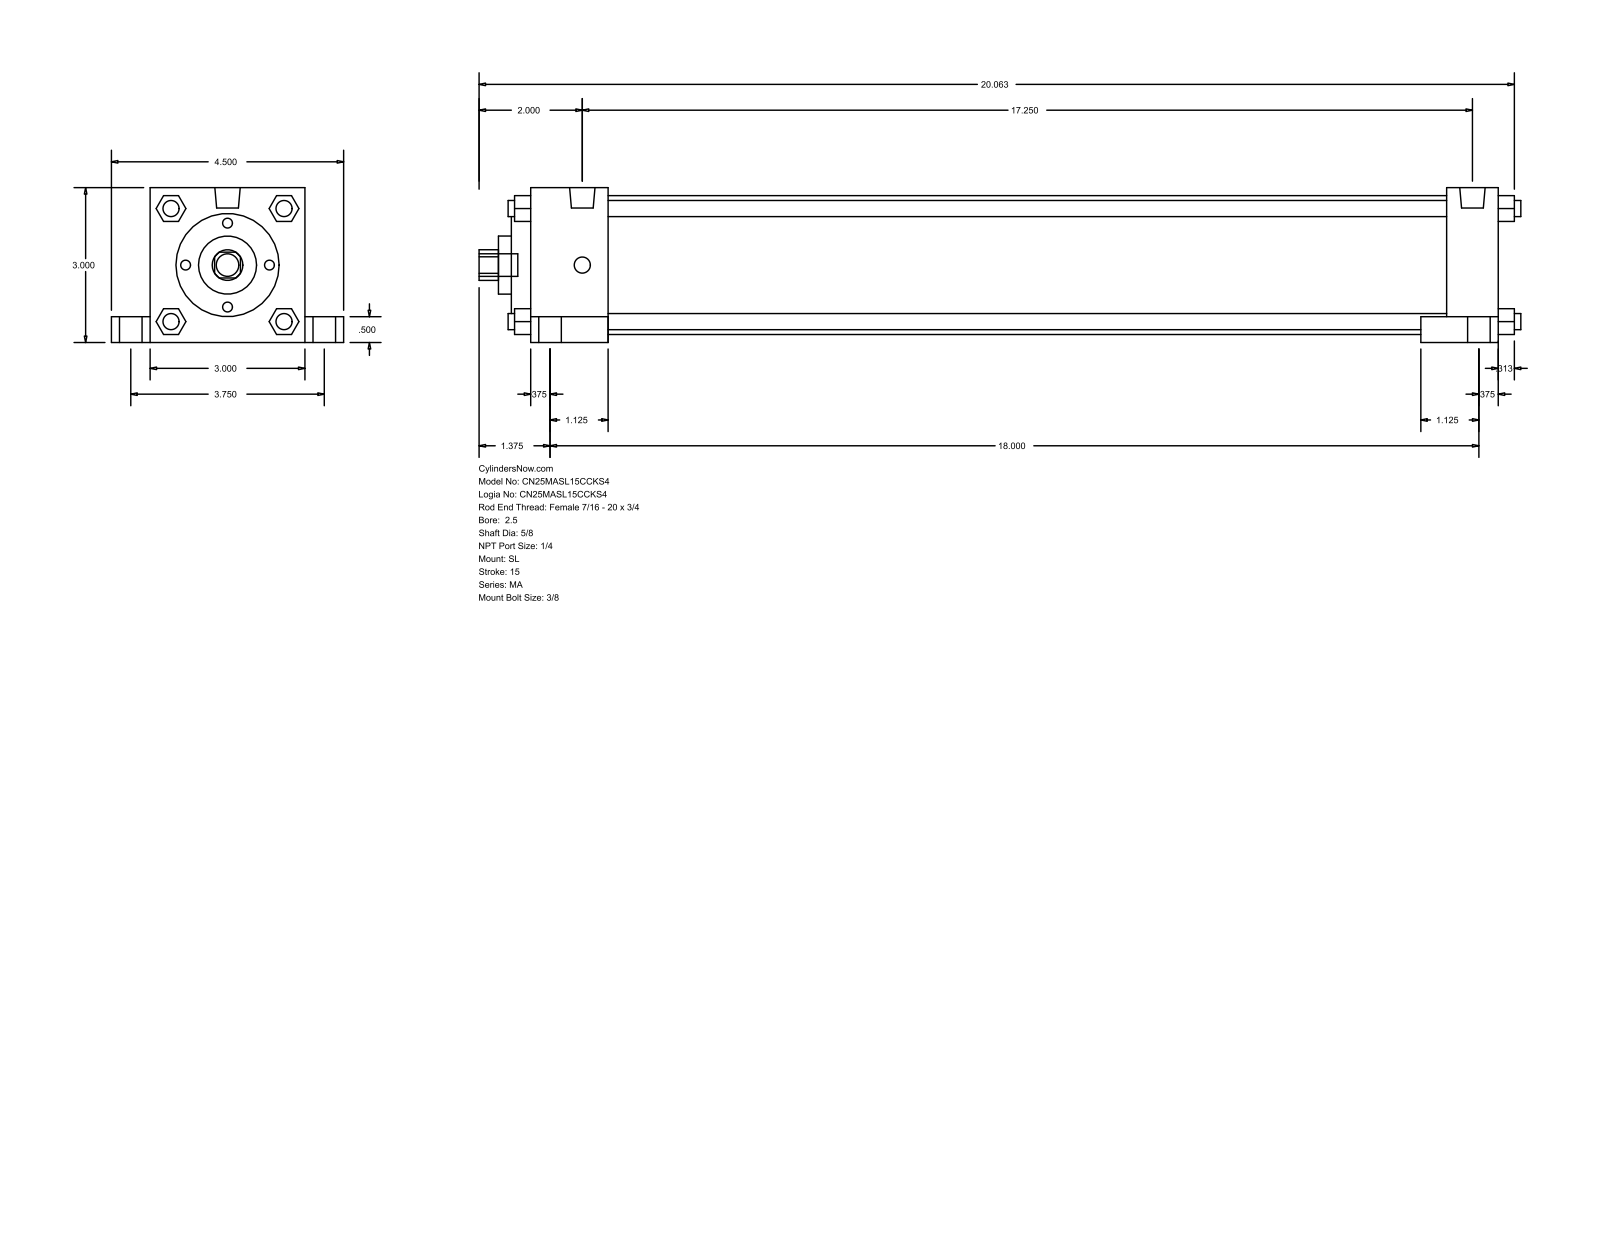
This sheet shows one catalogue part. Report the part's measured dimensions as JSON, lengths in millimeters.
{"part_name": "MA_SL__0250_0.625", "step_written_by": "GSSL Pune (CONFIG_CONTROL_DESIGN)", "units": "millimeters", "bodies": {"solids": 0, "faces": 150, "planar": 113, "cylindrical": 37, "other": 0}, "overall_size": [512.76, 114.3, 76.2], "round_holes": [[15.88, 1], [28.57, 1], [50.8, 1], [68.33, 1]], "round_bosses_or_shafts": [[7.94, 8], [11.11, 5], [17.46, 4], [12.49, 2]], "partial_cylinders_radius": [[7.54, 1]], "face_to_face_distances": [76.2, 476.25, 12.7, 412.75, 25.4, 38.1, 438.15, 450.85, 19.05, 63.5]}
